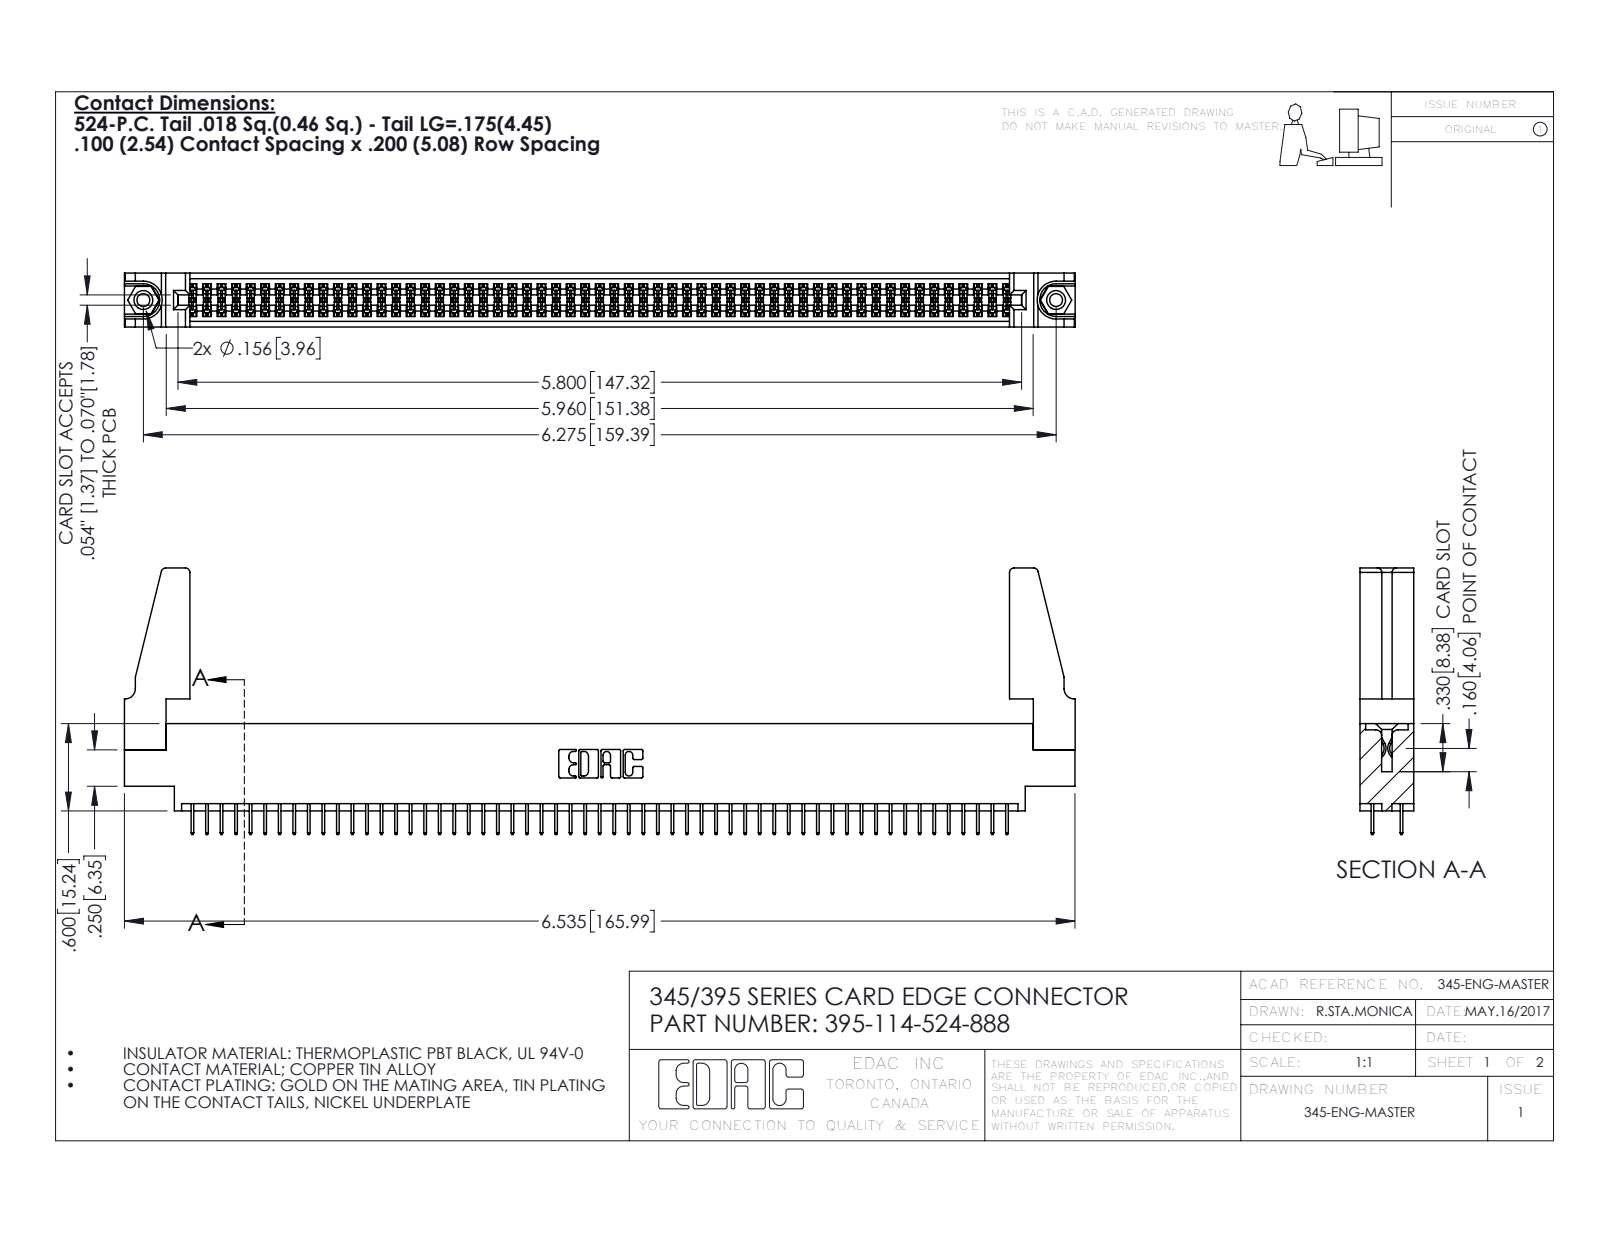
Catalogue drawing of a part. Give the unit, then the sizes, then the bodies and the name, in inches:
Units: inches
Overall size (bounding box): 6.536 × 1.832 × 0.37
Round holes (diameter × count): ⌀0.089 ×2, ⌀0.125 ×2, ⌀0.156 ×2, ⌀0.064 ×1
Round bosses / shafts (diameter × count): ⌀0.155 ×2
Partial cylindrical surfaces — rounded edges, fillets, slot ends (radius × count): R0.006 ×171, R0.01 ×22, R0.03 ×8, R0.007 ×6, R0.031 ×6, R0.026 ×3, R0.014 ×2, R0.019 ×2
Main face-to-face distances: 0.072, 0.298, 0.37, 0.2, 0.098, 0.272, 0.025, 0.225, 0.072, 0.175
Hole centre spacings: 0.27, 6.039, 6.275
Volume: 1.174 in³ · Surface area: 41.42 in²
Bodies: 119 solids, 6410 faces (4602 planar, 1792 cylindrical, 16 other)
Part name (STEP PRODUCT): 345-292-001_345-293-124; 395-114-524-888; 345-220-078_345-220-088; 345-250-001_345-250-001-102 (+1 more)
STEP written by: SolidWorks 2016 (CONFIG_CONTROL_DESIGN)
